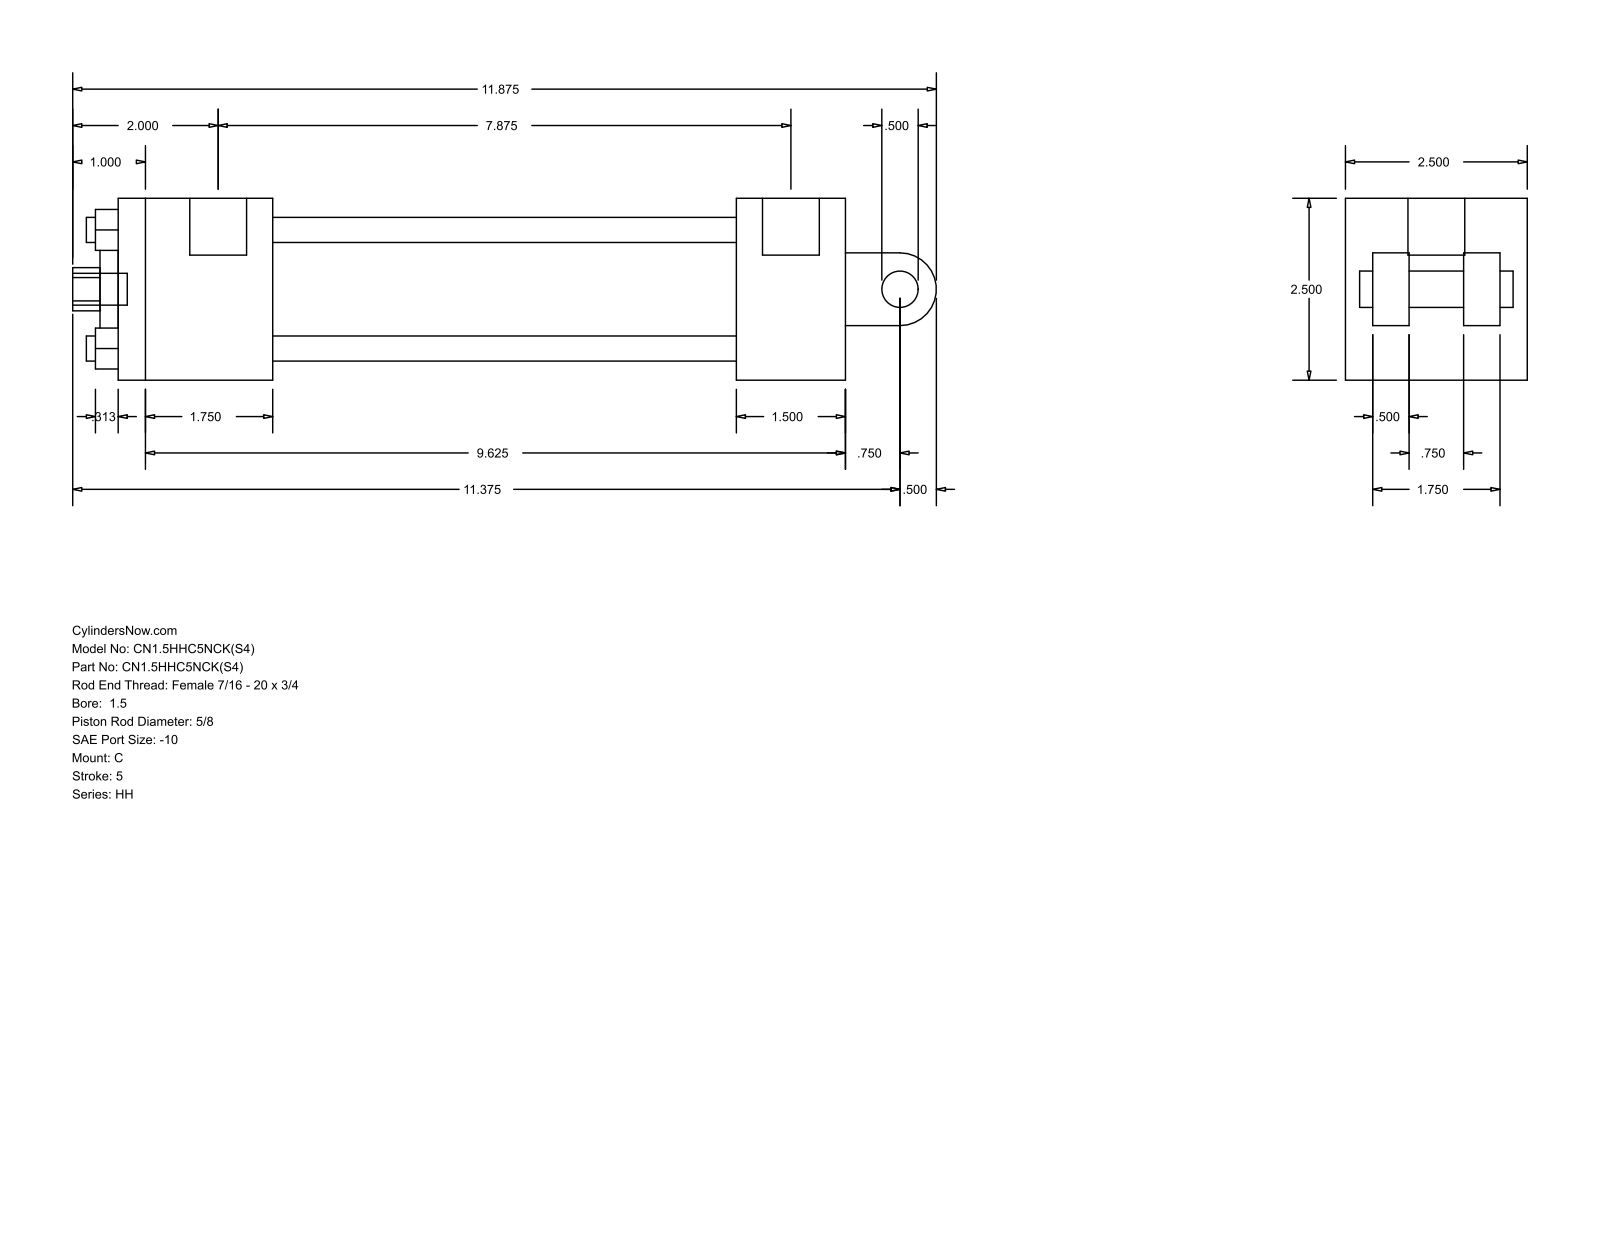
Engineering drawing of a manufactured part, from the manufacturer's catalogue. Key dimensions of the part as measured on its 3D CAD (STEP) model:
Part name (STEP PRODUCT): HH_C__0150_0.625
STEP written by: GSSL Pune (CONFIG_CONTROL_DESIGN)
Units: millimetres
Bodies: 0 solids, 99 faces (70 planar, 29 cylindrical, 0 other)
Overall size (bounding box): 301.62 × 63.5 × 63.5
Round holes (diameter × count): ⌀8.76 ×4, ⌀5.56 ×2, ⌀15.88 ×1, ⌀19.84 ×1, ⌀28.57 ×1, ⌀44.45 ×1
Round bosses / shafts (diameter × count): ⌀5.56 ×2, ⌀19.84 ×1, ⌀12.7 ×1, ⌀11.11 ×1
Partial cylindrical surfaces — rounded edges, fillets, slot ends (radius × count): R7.54 ×1, R12.7 ×1
Main face-to-face distances: 63.5, 254, 38.1, 53.97, 215.9, 161.93, 200.03, 12.7, 9.52, 19.05
Hole centre spacings: 29.27, 41.4, 58.55, 1.59
